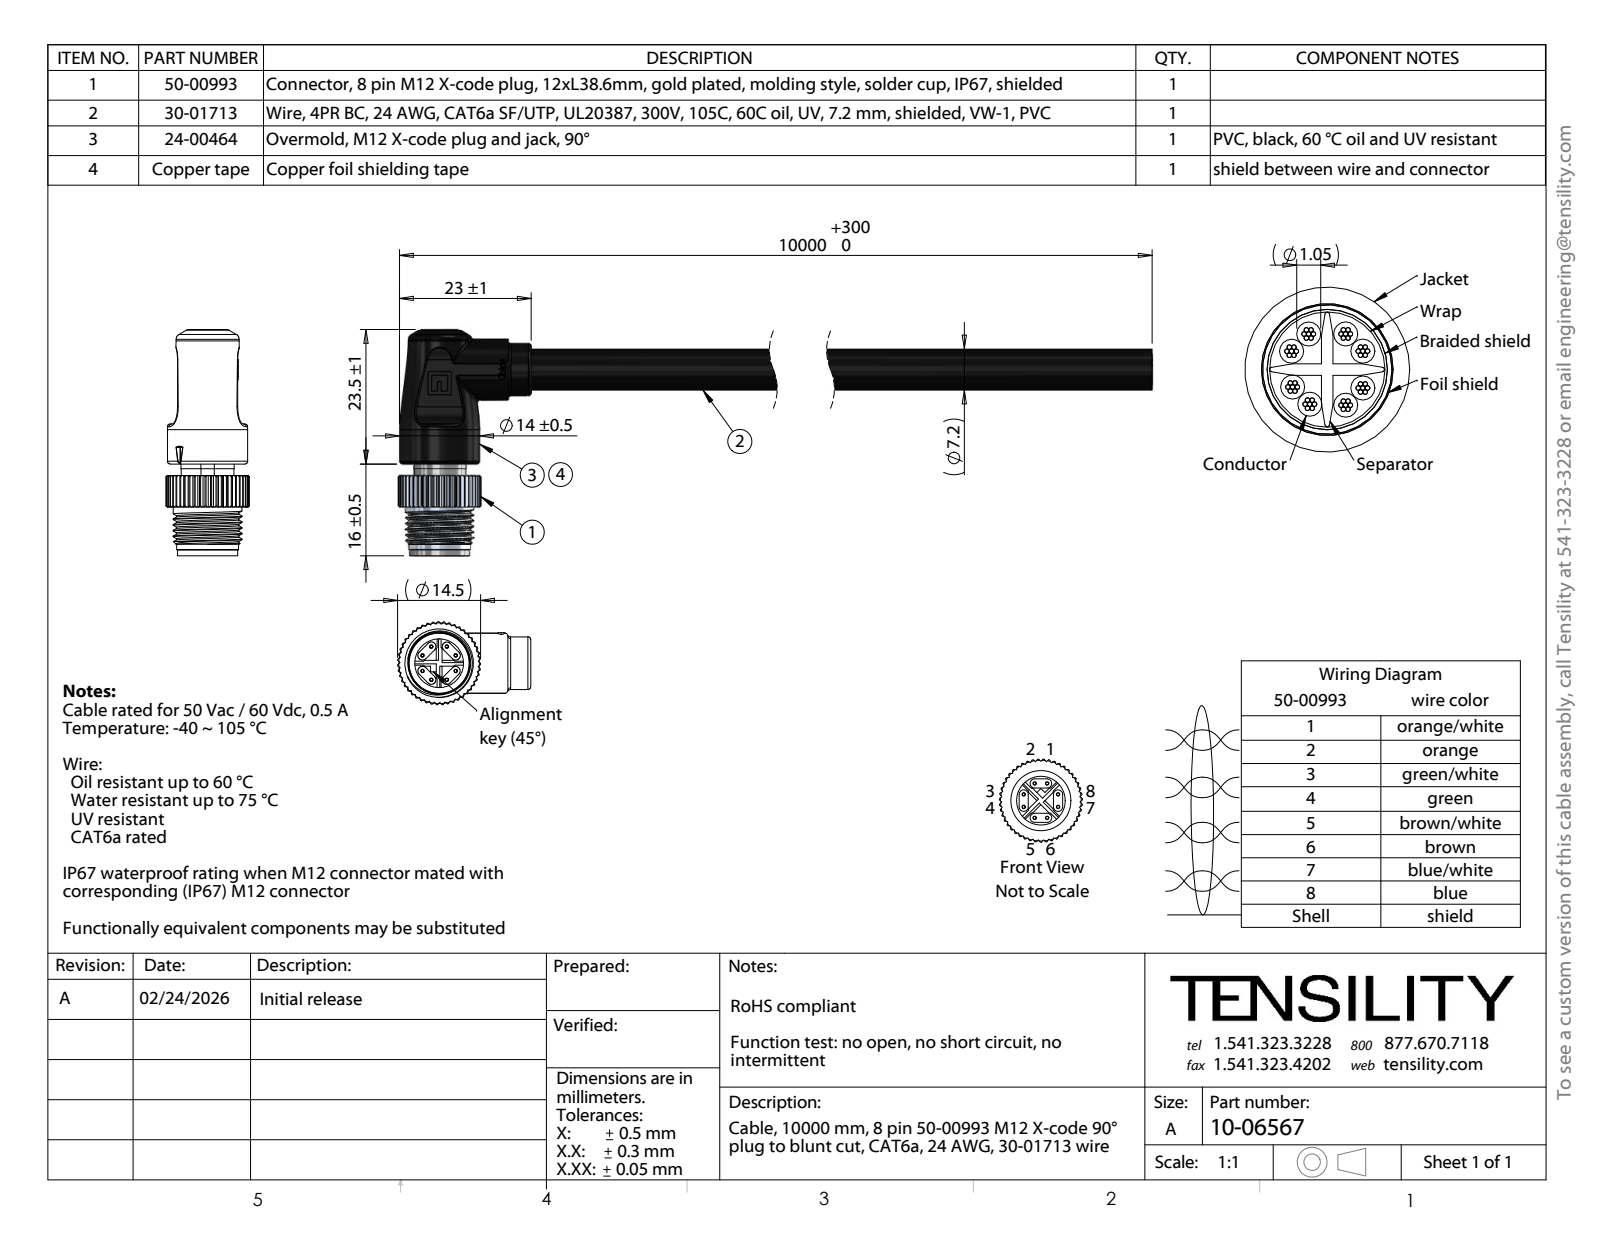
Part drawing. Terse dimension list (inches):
name: 50-00993-02; 50-00993-04_默认; 50-00993-01_STEP; 50-00993-05 (+5 more)
written by: SolidWorks 2025 (CONFIG_CONTROL_DESIGN)
unit: in
bodies: 85 solids, 1492 faces (552 planar, 617 cylindrical, 323 other)
size: 6.821 × 1.555 × 0.57
volume: 0.64 in³; area: 71.59 in²
holes: 56× ⌀0.008, 8× ⌀0.024, 8× ⌀0.047, 1× ⌀0.079, 1× ⌀0.098, 1× ⌀0.198, 1× ⌀0.207, 1× ⌀0.222, 1× ⌀0.226, 1× ⌀0.295, 1× ⌀0.335, 1× ⌀0.357
bosses: 8× ⌀0.055, 8× ⌀0.045, 8× ⌀0.041, 8× ⌀0.031, 2× ⌀0.362, 1× ⌀0.551, 1× ⌀0.472, 1× ⌀0.433
rounds: 12× R0.004, 8× R0.031, 8× R0.039, 6× R0.02, 4× R0.085, 1× R0.285
face distances: 0.02, 0.079, 0.039, 0.039, 0.236, 0.217, 0.197, 0.64, 0.659, 0.028
hole spacings: 0.014, 0.063, 0.07, 0.126, 0.016, 0.042, 0.056, 0.076
